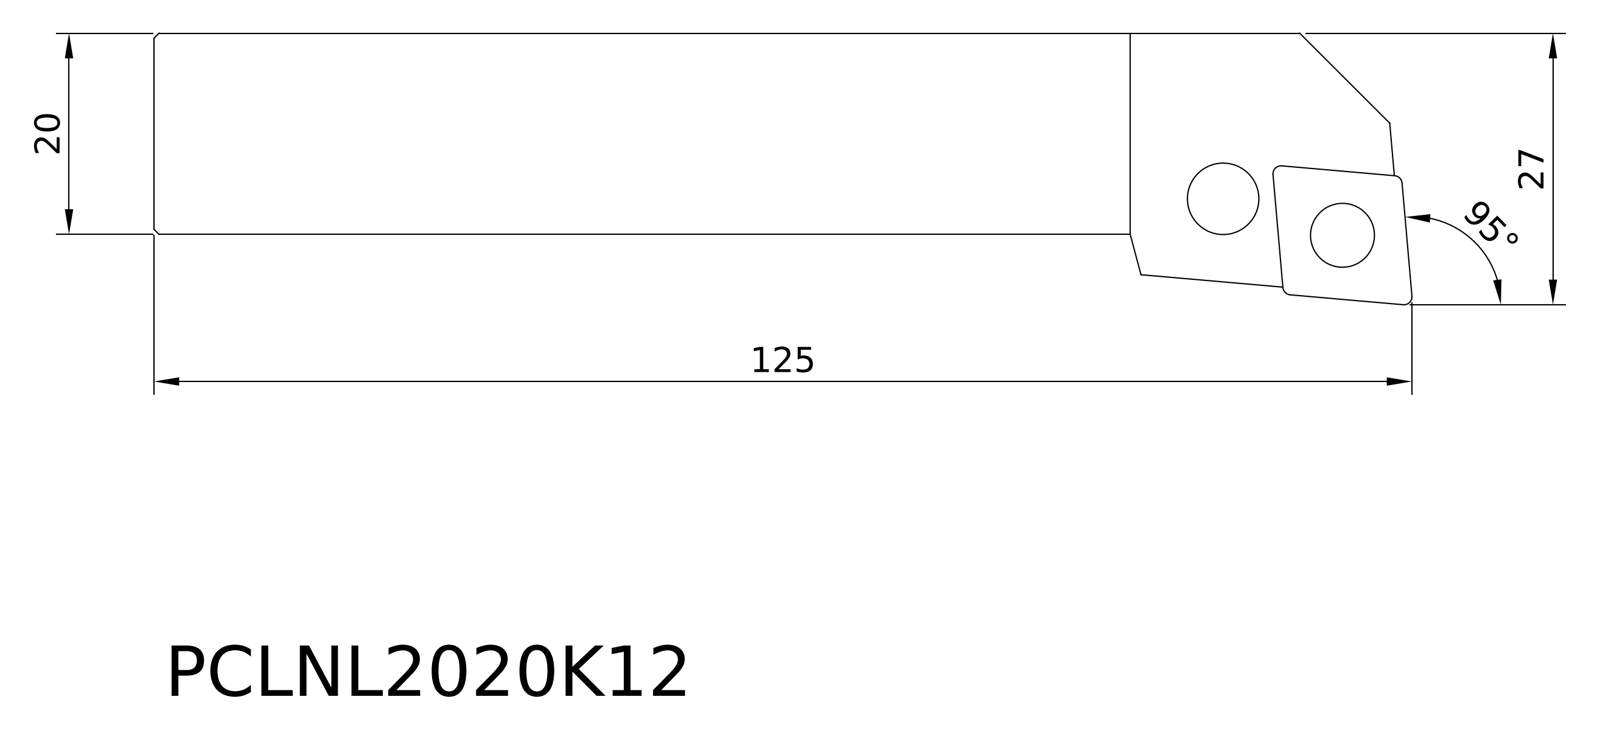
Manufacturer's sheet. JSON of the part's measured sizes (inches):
{"part_name": "PCLNL2020K12; 1648_MIR; 3612_MIR; CNMG 120408_MIR (+1 more)", "step_written_by": "Autodesk Inventor 2013 (AUTOMOTIVE_DESIGN)", "units": "inches", "bodies": {"solids": 5, "faces": 357, "planar": 225, "cylindrical": 23, "other": 109}, "overall_size": [4.921, 0.984, 0.968], "volume_in3": 3.13, "surface_area_in2": 20.7, "round_holes": [[0.157, 1], [0.197, 1], [0.276, 1]], "round_bosses_or_shafts": [[0.315, 1], [0.146, 1]], "partial_cylinders_radius": [[0.031, 4], [0.039, 4], [0.079, 2], [0.081, 2], [0.236, 2], [0.091, 1], [0.118, 1], [0.12, 1]], "face_to_face_distances": [0.787, 0.187, 0.022, 0.313, 0.125, 0.312, 0.125, 0.478, 0.479, 0.022], "hole_center_spacings": [0.284, 0.321, 0.472]}
